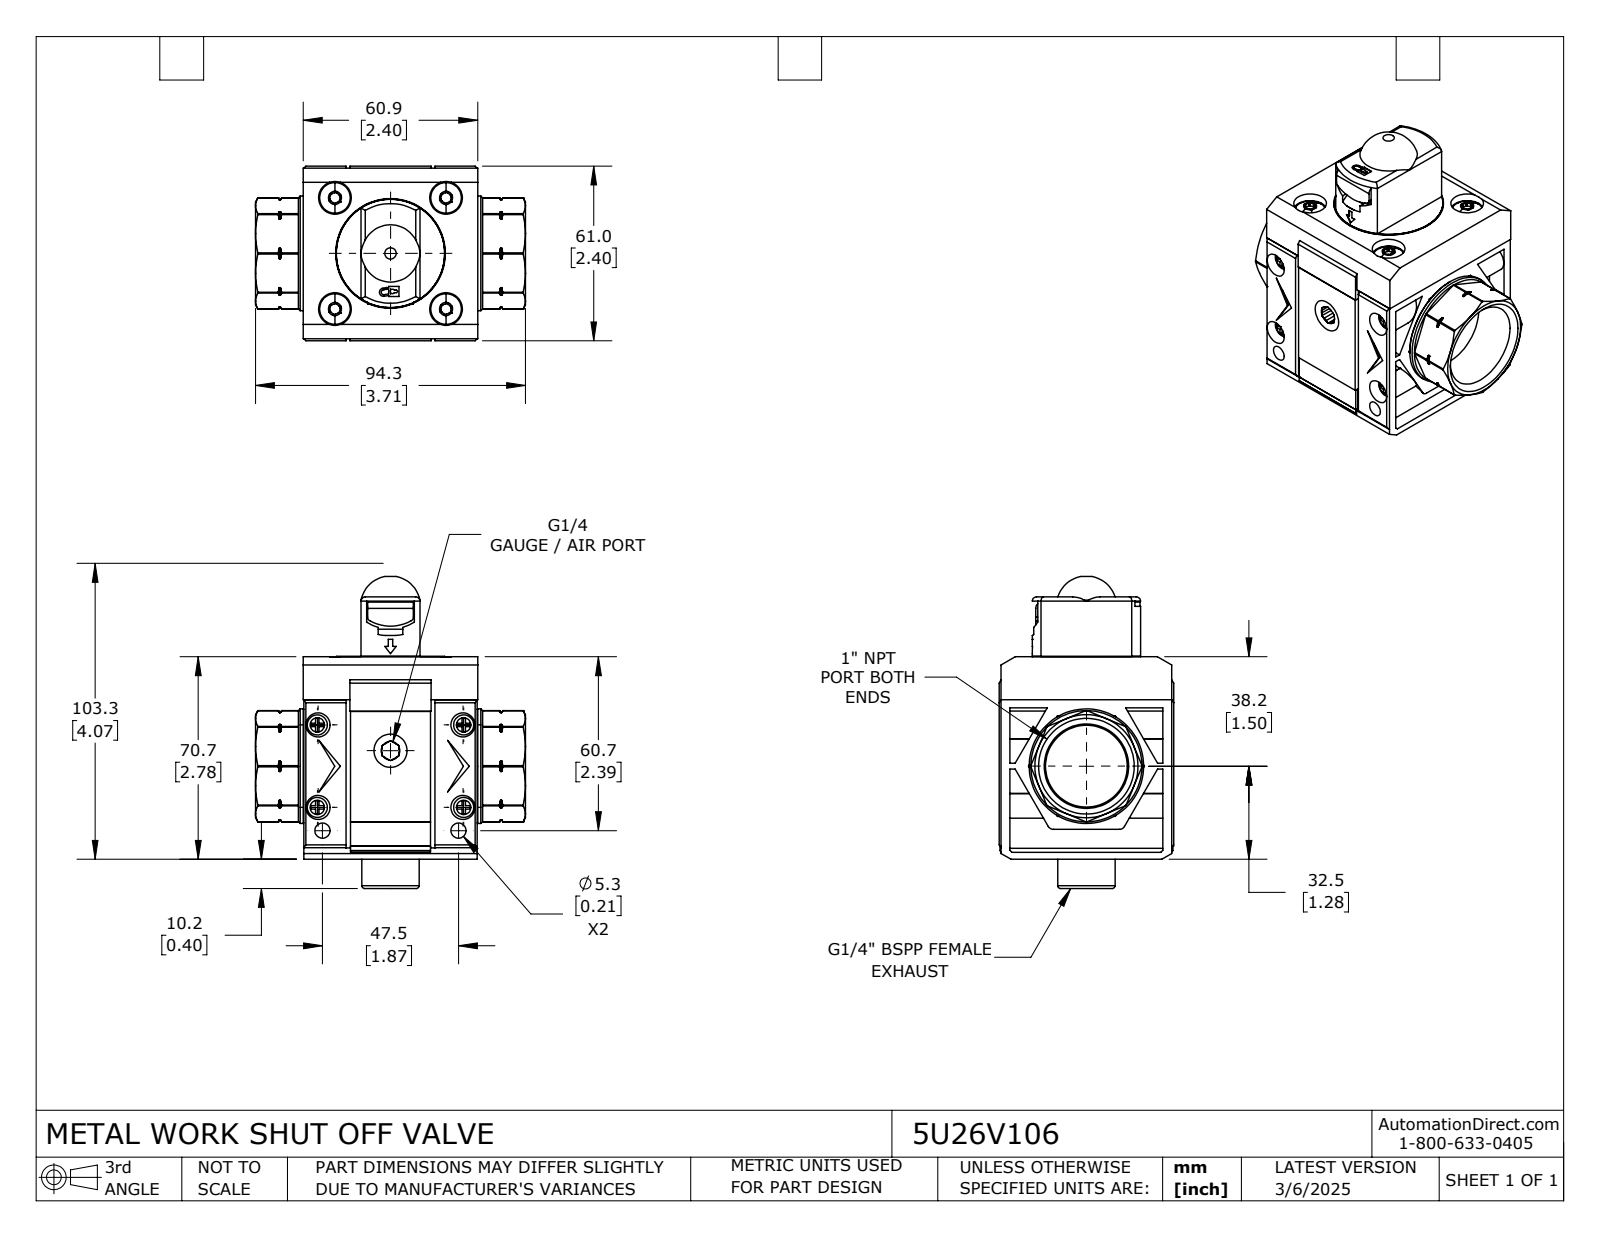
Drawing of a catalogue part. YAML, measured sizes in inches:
part_name: "5U26V106"
step_written_by: "SolidWorks 2024 (CONFIG_CONTROL_DESIGN)"
units: inches
bodies: {solids: 13, faces: 968, planar: 458, cylindrical: 268, other: 242}
overall_size: [4.288, 3.713, 2.402]
volume: 15.82
surface_area: 121
round_holes:
  - {diameter: 0.128, count: 4}
  - {diameter: 0.165, count: 4}
  - {diameter: 0.331, count: 4}
  - {diameter: 0.449, count: 4}
  - {diameter: 0.209, count: 2}
  - {diameter: 0.451, count: 1}
  - {diameter: 0.457, count: 1}
  - {diameter: 0.787, count: 1}
  - {diameter: 1.508, count: 1}
round_bosses_or_shafts:
  - {diameter: 0.276, count: 4}
  - {diameter: 0.189, count: 4}
  - {diameter: 0.15, count: 4}
  - {diameter: 1.575, count: 1}
  - {diameter: 1.496, count: 1}
  - {diameter: 1.378, count: 1}
  - {diameter: 1.248, count: 1}
  - {diameter: 1.035, count: 1}
partial_cylinders:
  - {radius: 0.011, count: 24}
  - {radius: 0.059, count: 4}
  - {radius: 0.069, count: 4}
  - {radius: 0.191, count: 4}
  - {radius: 0.079, count: 2}
  - {radius: 0.242, count: 2}
  - {radius: 0.591, count: 2}
  - {radius: 0.018, count: 1}
face_to_face_distances: [0.094, 2.39, 2.193, 2.098, 0.299, 2.402, 0.028, 1.799, 2.319, 2.382]
hole_center_spacings: [1.08, 1.528, 0.325, 1.057, 1.134, 1.265, 1.443, 1.454]
